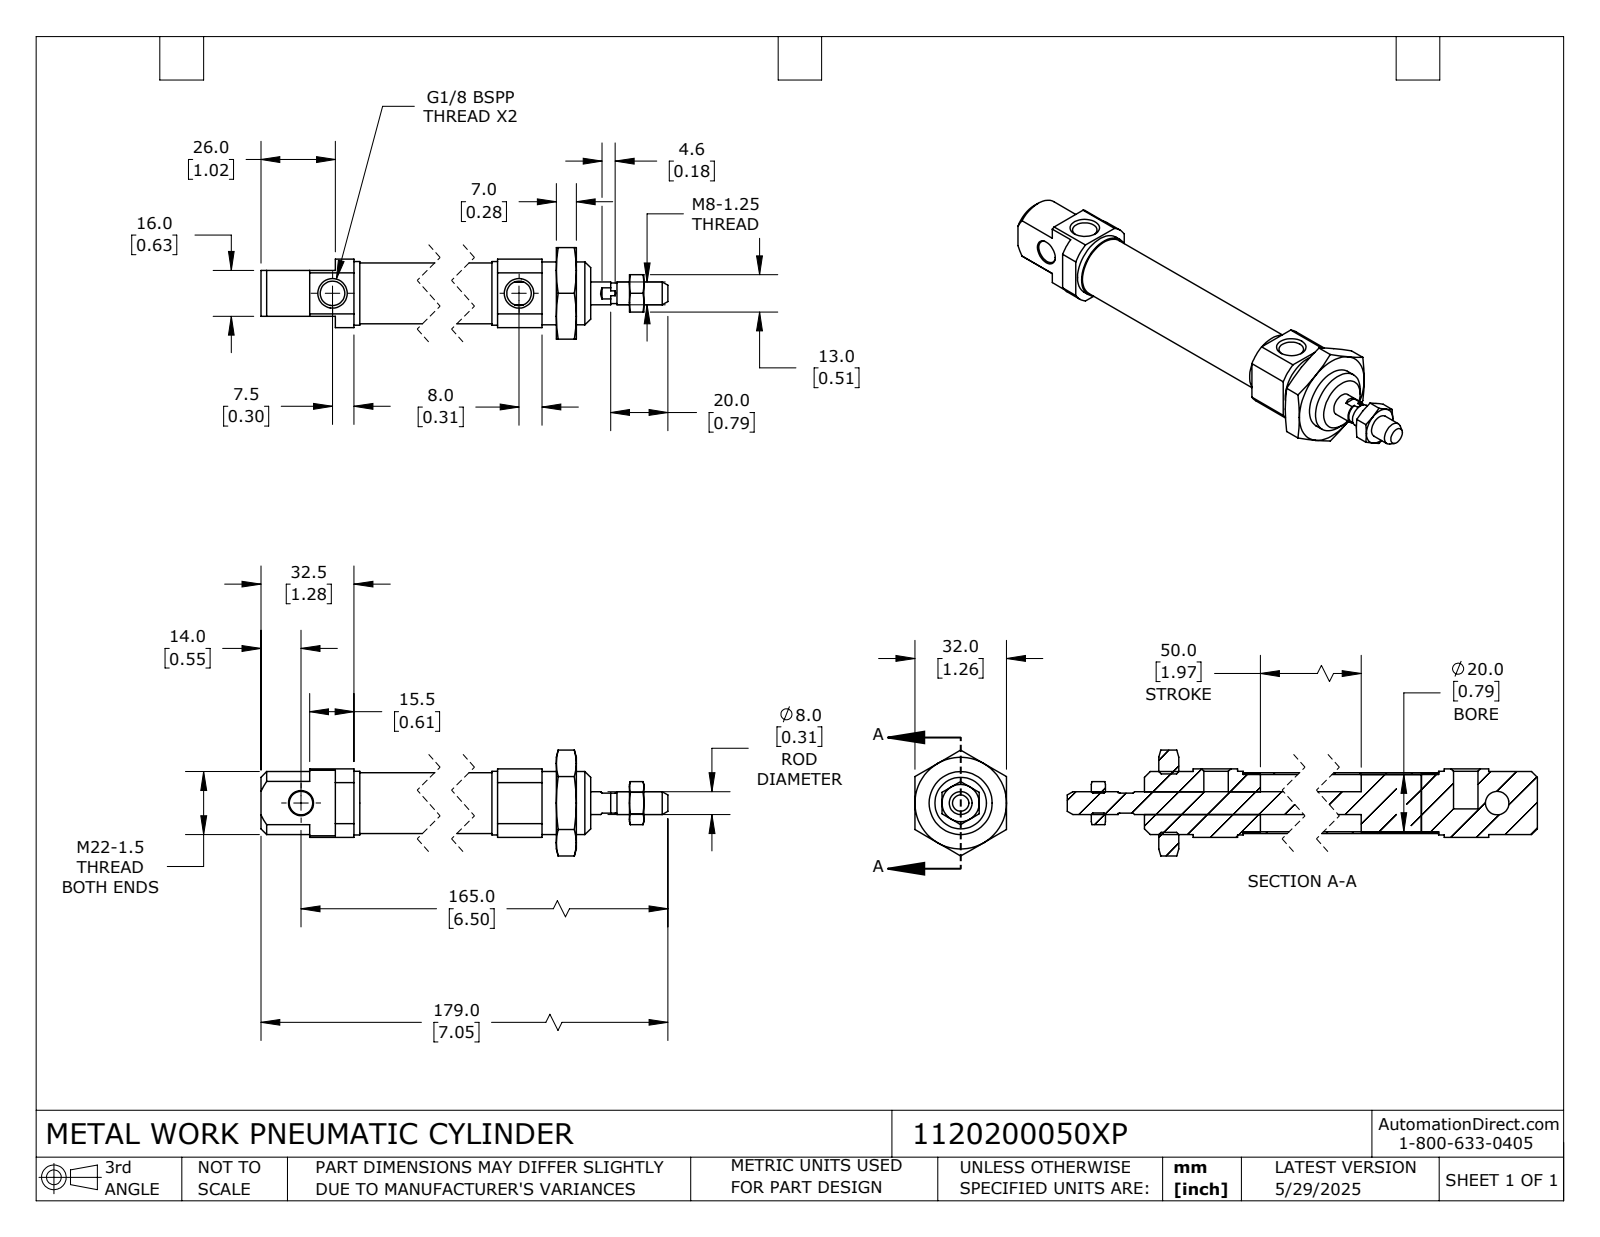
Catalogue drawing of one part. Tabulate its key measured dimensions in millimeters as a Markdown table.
| quantity | value |
| --- | --- |
| part name | 1120200050XP; 1120200050XP_BODY; 1120200050XP_ROD |
| STEP written by | SolidWorks 2024 (CONFIG_CONTROL_DESIGN) |
| units | millimeters |
| bodies | 6 solids, 147 faces (56 planar, 45 cylindrical, 46 other) |
| overall size | 179 × 36.95 × 32 |
| volume | 48 277 mm³ |
| surface area | 28 101 mm² |
| round holes (diameter × count) | 8.57 × 2, 6.92 × 1, 8.2 × 1, 20 × 1, 20.38 × 1 |
| round bosses / shafts (diameter × count) | 22.2 × 1, 22 × 1, 21.27 × 1, 20.15 × 1, 8 × 1, 7.2 × 1 |
| partial cylindrical surfaces (radius × count) | 13.95 × 1 |
| main face-to-face distances | 3.97, 19.97, 23.94, 8, 40.5, 111.5, 7, 5, 106.5, 99.5 |
| hole center spacings | 102 |
